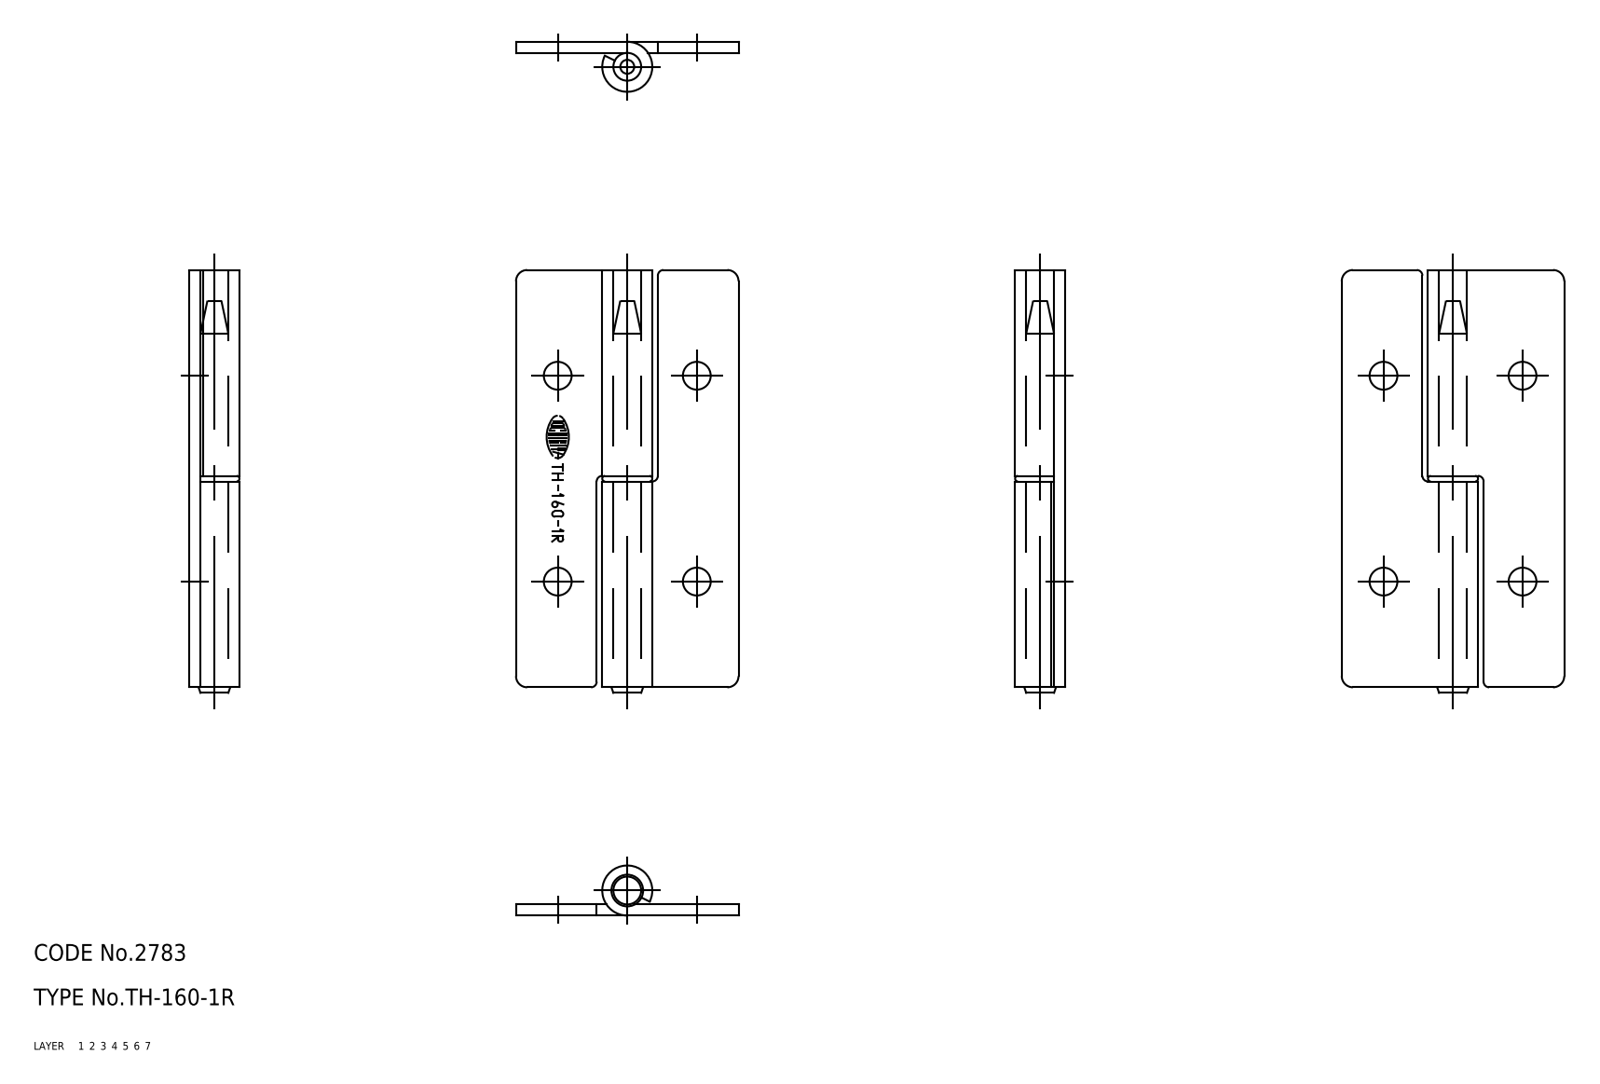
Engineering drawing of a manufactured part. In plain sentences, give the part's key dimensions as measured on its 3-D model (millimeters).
The part is named "67112049; 67112062; 67112075". Its 3-D file was written by "CADfix (AUTOMOTIVE_DESIGN)". It is 3 solids with 53 faces: 0 planar, 0 cylindrical and 53 other. Overall it measures 76 by 40 by 9 millimeters. Its volume is 9 063 cubic millimeters and its surface area 9 908 square millimeters.
